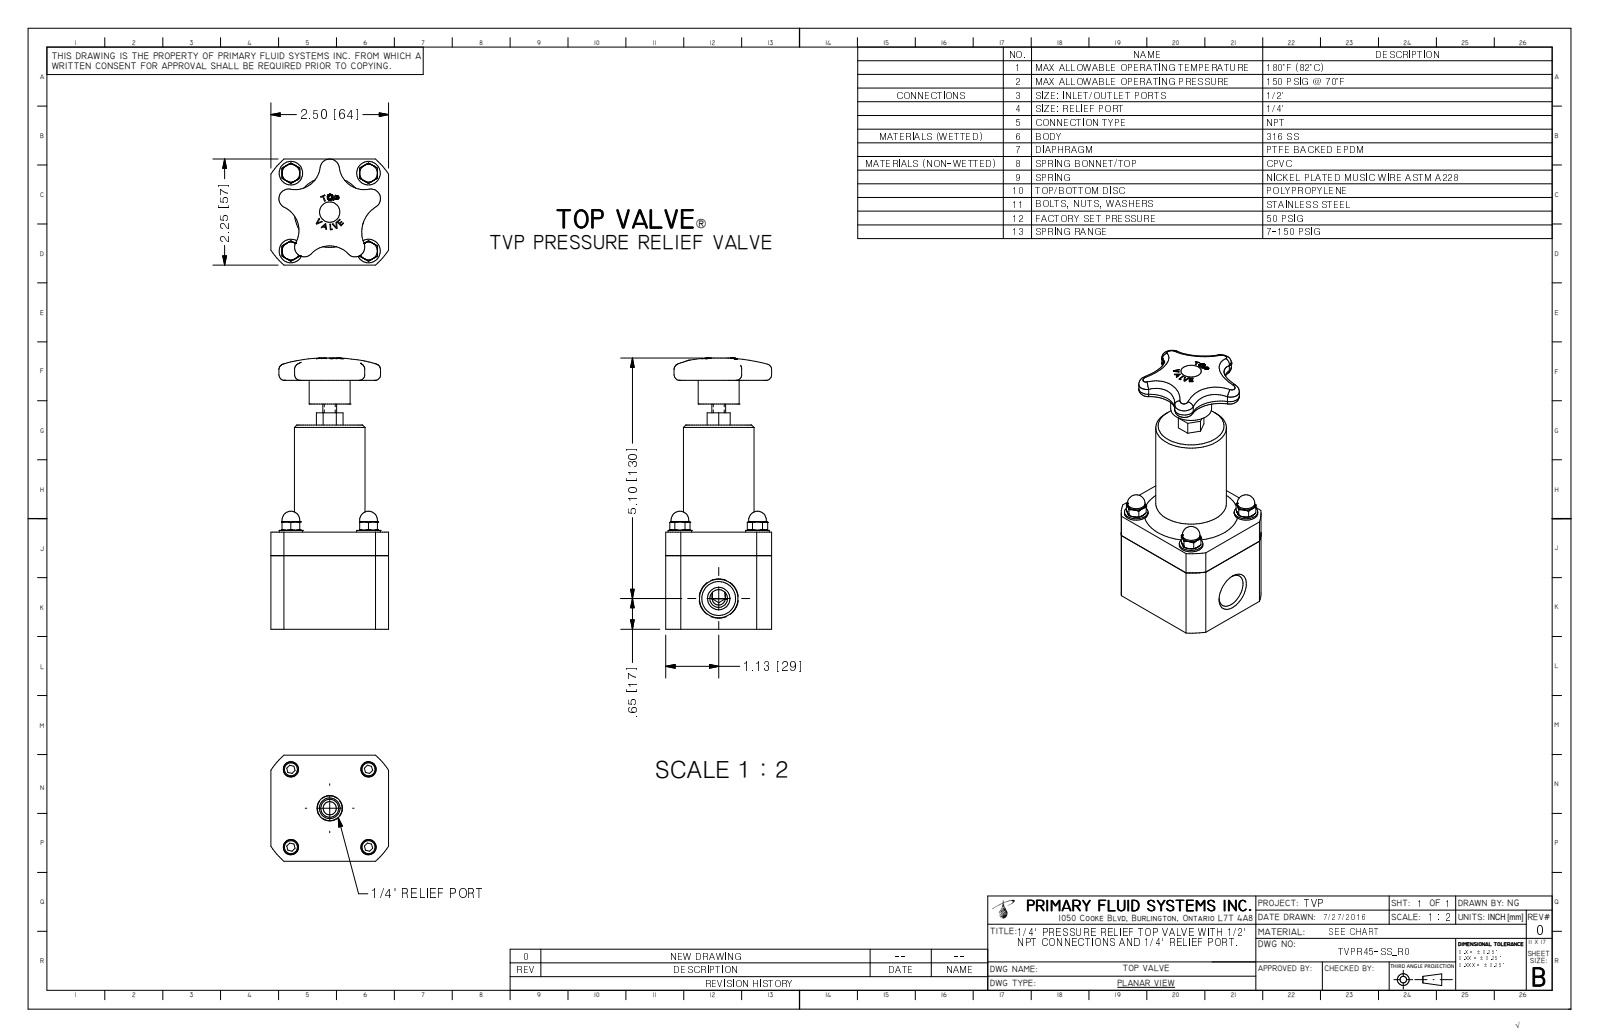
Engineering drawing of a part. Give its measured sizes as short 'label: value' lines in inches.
name: TVPR45-SS_R0
written by: Autodesk Inventor 2009 (AUTOMOTIVE_DESIGN)
unit: in
bodies: 1 solid, 356 faces (147 planar, 48 cylindrical, 161 other)
size: 5.75 × 2.5 × 2.25
volume: 16.1 in³; area: 57.37 in²
holes: 4× ⌀0.147, 1× ⌀0.437, 1× ⌀0.719, 1× ⌀1.525
bosses: 4× ⌀0.5, 4× ⌀0.375, 4× ⌀0.312, 1× ⌀1.5, 1× ⌀0.87, 1× ⌀0.293
rounds: 5× R0.085, 5× R0.205, 4× R0.536, 4× R0.656, 1× R0.625, 1× R0.745, 1× R1.488
face distances: 2.25, 2.5, 2.06, 4.33, 2.27, 0.6, 1.9, 4.776, 2.716, 0.446
hole spacings: 1.167, 1.167, 1.65, 1.65, 2.334
